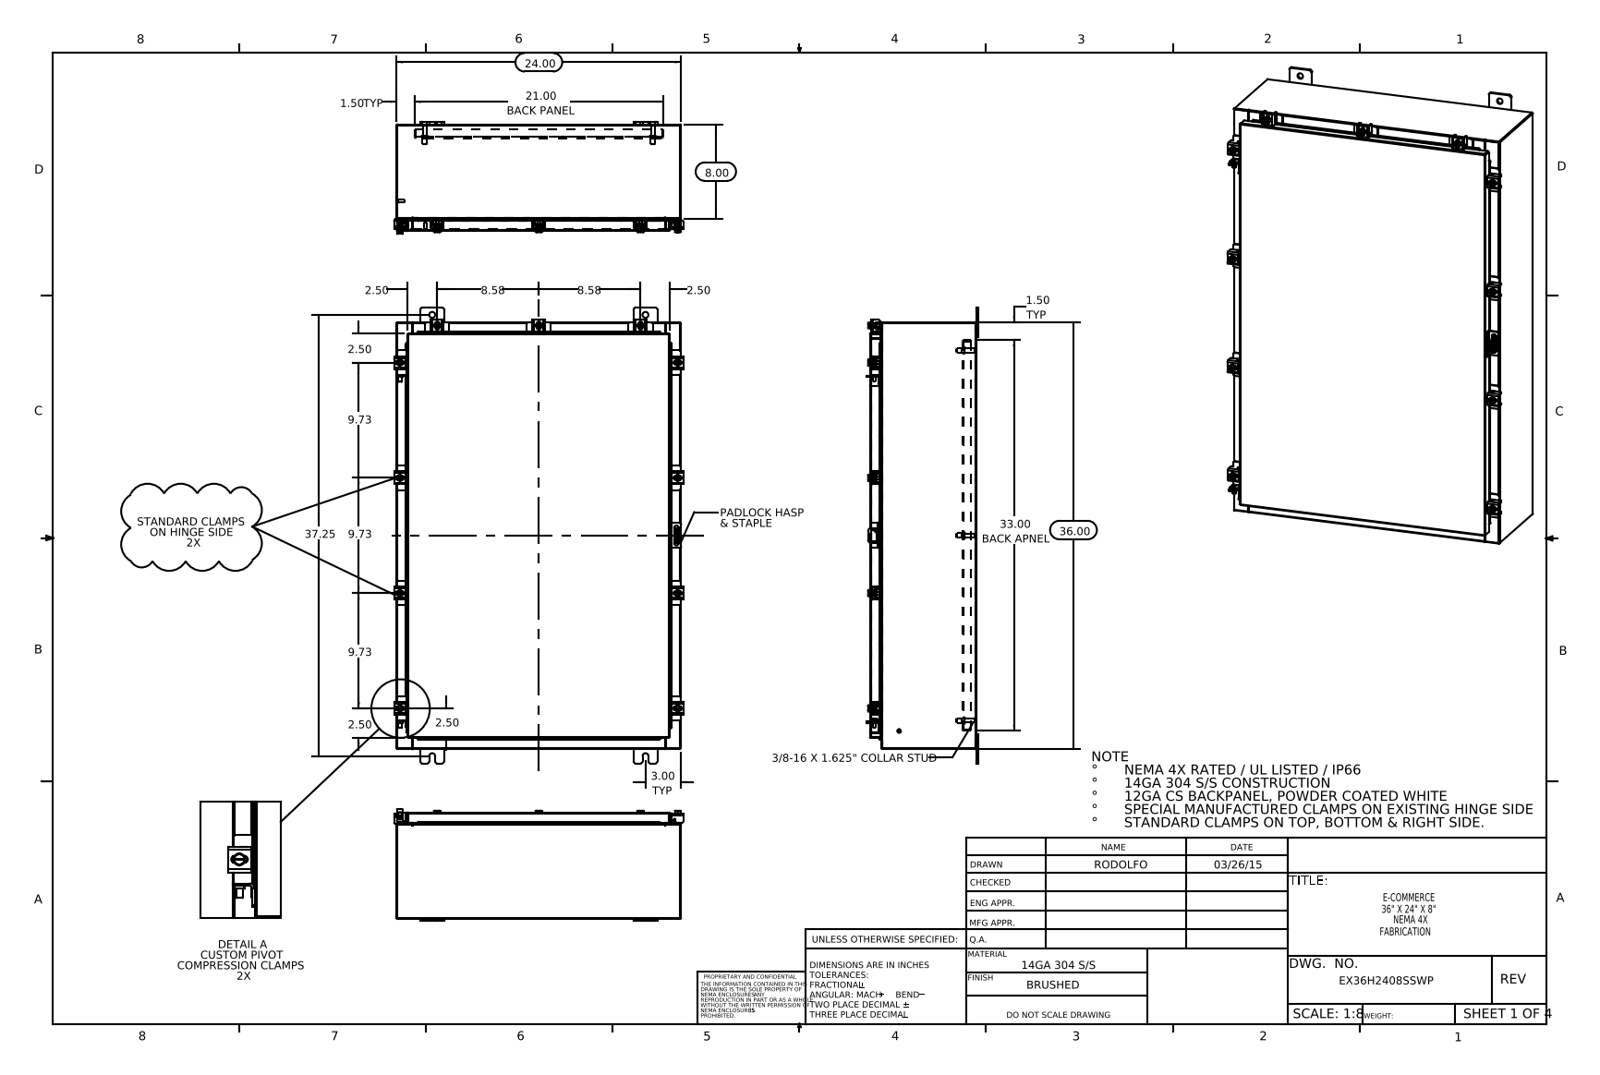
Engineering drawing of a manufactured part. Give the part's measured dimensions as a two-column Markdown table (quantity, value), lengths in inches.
| quantity | value |
| --- | --- |
| part name | EX36H2408SSWP Cover; Quarter-20 CD Stud; 22101002_RTP29; EX36H2408SSWP (+8 more) |
| STEP written by | SolidWorks 2014 (CONFIG_CONTROL_DESIGN) |
| units | inches |
| bodies | 78 solids, 1971 faces (1041 planar, 758 cylindrical, 172 other) |
| overall size | 38.5 × 24.421 × 9.453 |
| volume | 308.1 in³ |
| surface area | 7 633 in² |
| round holes (diameter × count) | 0.213 × 11, 0.26 × 11, 0.5 × 10, 0.125 × 1, 0.25 × 1 |
| round bosses / shafts (diameter × count) | 0.5 × 11, 0.25 × 11, 0.399 × 9, 0.625 × 6, 0.375 × 6, 0.33 × 6, 0.315 × 2, 0.236 × 2 |
| partial cylindrical surfaces (radius × count) | 0.06 × 48, 0.013 × 26, 0.19 × 24, 0.088 × 22, 0.141 × 22, 0.09 × 20, 0.12 × 20, 0.05 × 19 |
| main face-to-face distances | 0.075, 8.9, 8.975, 8.826, 0.104, 1, 1.075, 7.826, 7.9, 1.179 |
| hole center spacings | 25.389, 5.299, 9.73, 10.964, 14.744, 15.625, 19.459, 20.597 |
